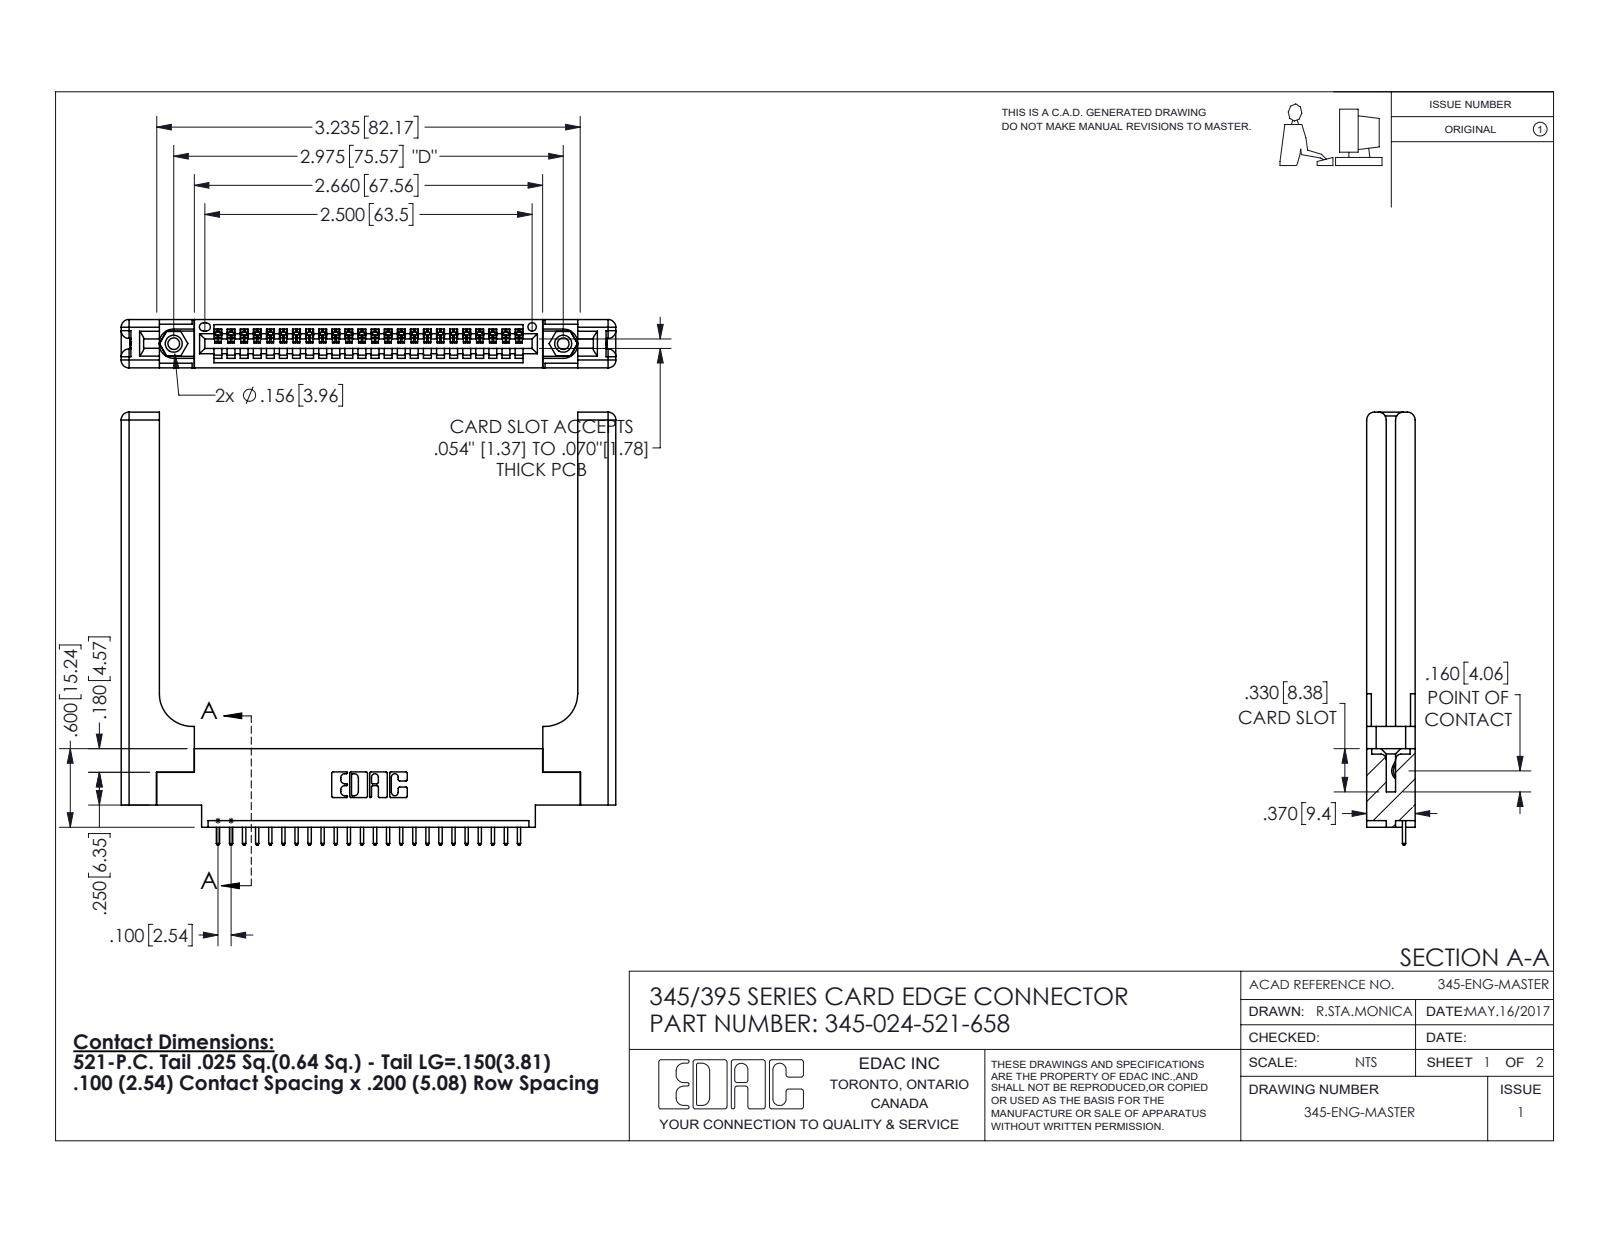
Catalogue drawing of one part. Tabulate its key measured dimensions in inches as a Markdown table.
| quantity | value |
| --- | --- |
| part name | 345-024-521-658; 345-250-001_345-250-001-102; 345-292-001_345-293-121; 345-220-058_345-220-058 (+1 more) |
| STEP written by | SolidWorks 2016 (CONFIG_CONTROL_DESIGN) |
| units | inches |
| bodies | 29 solids, 1778 faces (1192 planar, 526 cylindrical, 60 other) |
| overall size | 3.779 × 3.307 × 0.37 |
| volume | 1.055 in³ |
| surface area | 25.73 in² |
| round holes (diameter × count) | 0.089 × 2, 0.125 × 2, 0.156 × 2, 0.064 × 1 |
| round bosses / shafts (diameter × count) | 0.155 × 2 |
| partial cylindrical surfaces (radius × count) | 0.006 × 48, 0.01 × 48, 0.01 × 22, 0.06 × 16, 0.007 × 6, 0.031 × 6, 0.026 × 3, 0.03 × 2 |
| main face-to-face distances | 0.37, 0.072, 0.298, 0.148, 0.15, 0.077, 0.098, 0.272, 0.025, 0.2 |
| hole center spacings | 0.27, 2.741, 2.975 |
